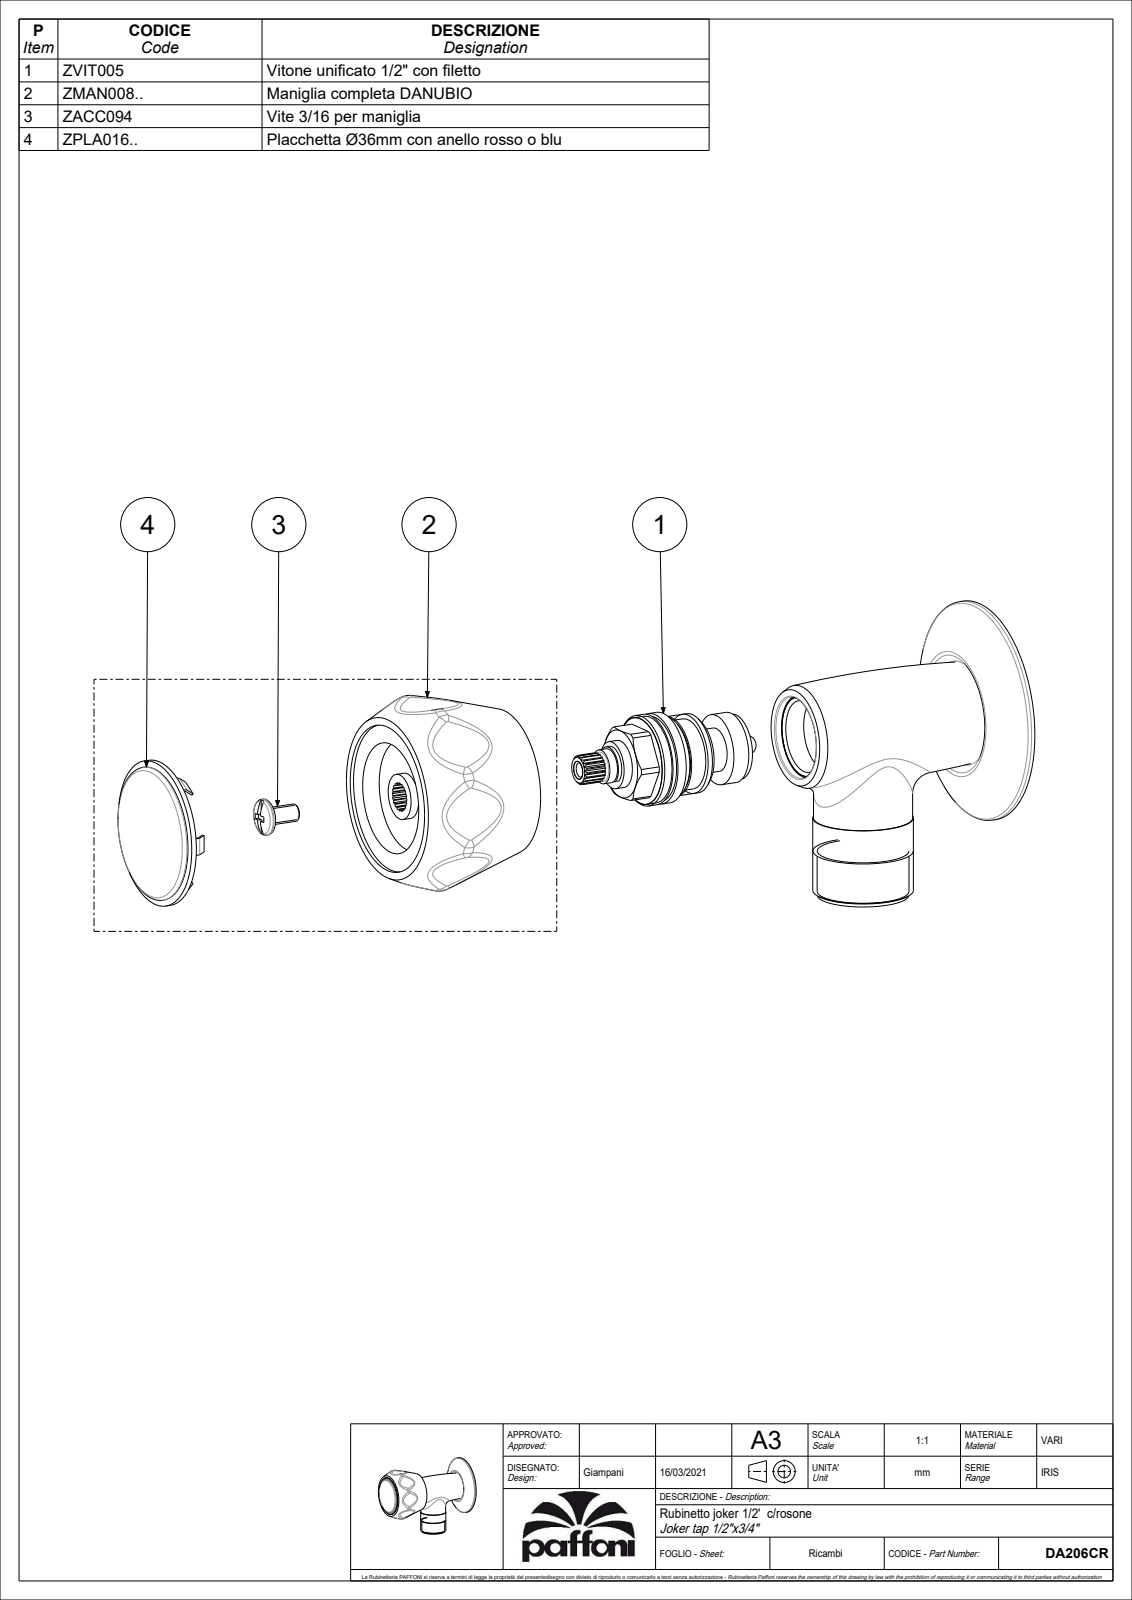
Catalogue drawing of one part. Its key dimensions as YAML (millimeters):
part_name: "DA206CR"
step_written_by: "CREO PARAMETRIC BY PTC INC, 2020044 (CONFIG_CONTROL_DESIGN)"
units: millimeters
bodies: {solids: 1, faces: 102, planar: 8, cylindrical: 20, other: 74}
overall_size: [99.5, 74.5, 58]
volume: 124912
surface_area: 20396
round_bosses_or_shafts:
  - {diameter: 58, count: 1}
  - {diameter: 38.5, count: 1}
  - {diameter: 26.4, count: 1}
  - {diameter: 26, count: 1}
  - {diameter: 24, count: 1}
  - {diameter: 21, count: 1}
partial_cylinders:
  - {radius: 21.31, count: 8}
face_to_face_distances: [54.1, 89.4, 35.3, 6.7, 60.8, 96.1, 96.5, 89.8, 35.7, 0.4]
